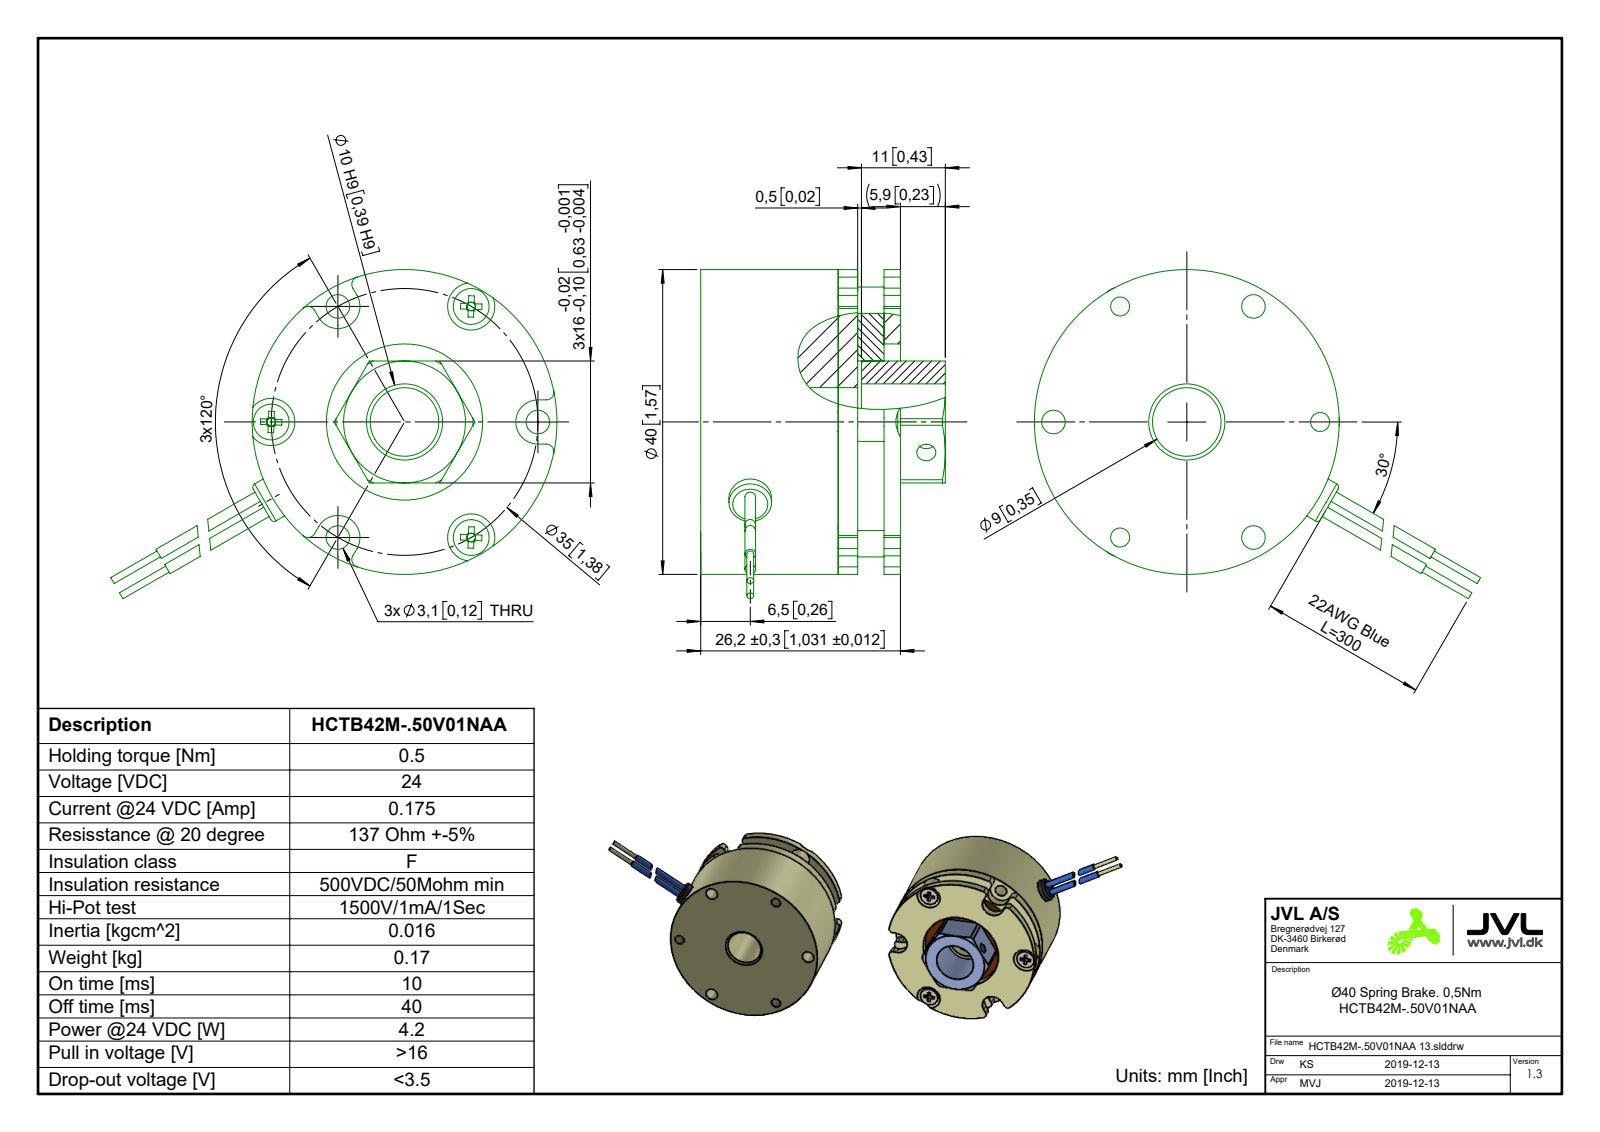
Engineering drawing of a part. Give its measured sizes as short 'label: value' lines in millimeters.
name: HCTB42M-.50V01NAA 11
written by: SolidWorks 2018 (AUTOMOTIVE_DESIGN)
unit: mm
bodies: 12 solids, 288 faces (111 planar, 104 cylindrical, 73 other)
size: 40.05 × 40 × 32.1
volume: 27 036 mm³; area: 14 809 mm²
holes: 6× ⌀3.2, 5× ⌀2.5, 3× ⌀2.6, 2× ⌀0.8, 1× ⌀9, 1× ⌀10, 1× ⌀20.5
bosses: 3× ⌀5.1, 3× ⌀4.7, 1× ⌀40, 1× ⌀27, 1× ⌀5.6
rounds: 6× R1, 3× R3, 1× R9
face distances: 5.6, 3.2, 2.15, 8.8, 15.25, 18.45, 24.05, 15.4, 3.05, 8.65
hole spacings: 17.5, 30.31, 35, 23.63, 2.3
